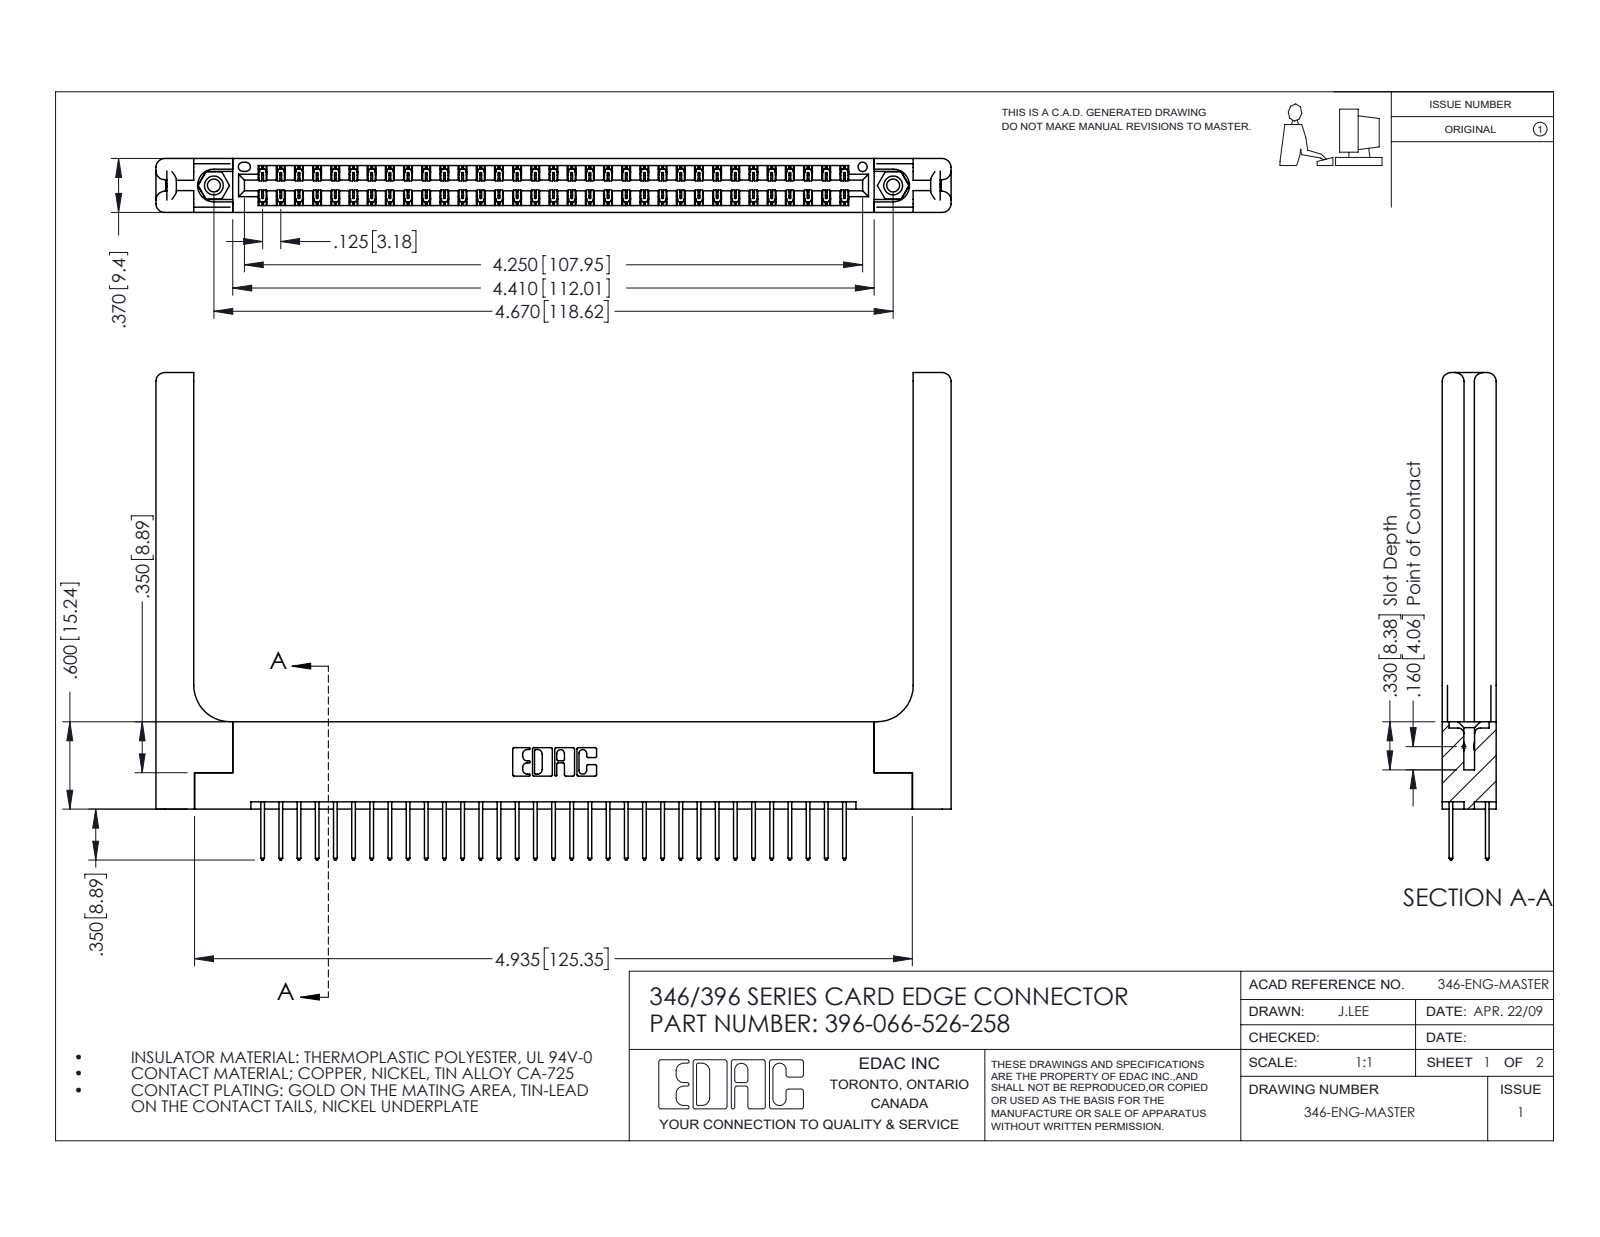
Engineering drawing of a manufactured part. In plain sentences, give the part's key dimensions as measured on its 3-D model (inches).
The part is named "346-220-058_345-220-058; 396-066-526-258; 345-250-001_345-250-001-102; 345-292-001_345-293-126 (+1 more)". Its 3-D file was written by "SolidWorks 2016 (CONFIG_CONTROL_DESIGN)". It is 71 solids with 3810 faces: 2534 planar, 1216 cylindrical and 60 other. Overall it measures 5.466 by 3.35 by 0.37 inches. Its volume is 1.286 cubic inches and its surface area 37.17 square inches. Round holes: 2 of diameter 0.089, 2 of diameter 0.125, 2 of diameter 0.156, 1 of diameter 0.064. Round bosses or shafts: 2 of diameter 0.155. Partial cylindrical surfaces (rounded edges, fillets, slot ends): 99 of radius 0.006, 66 of radius 0.01, 22 of radius 0.01, 16 of radius 0.06, 6 of radius 0.007, 6 of radius 0.031, 3 of radius 0.026, 2 of radius 0.014. The main face-to-face distances are 0.37, 0.048, 0.322, 0.072, 0.25, 0.148, 0.15, 0.025, 0.298, 0.275. The hole center spacings are 0.246, 4.462, 4.67.
